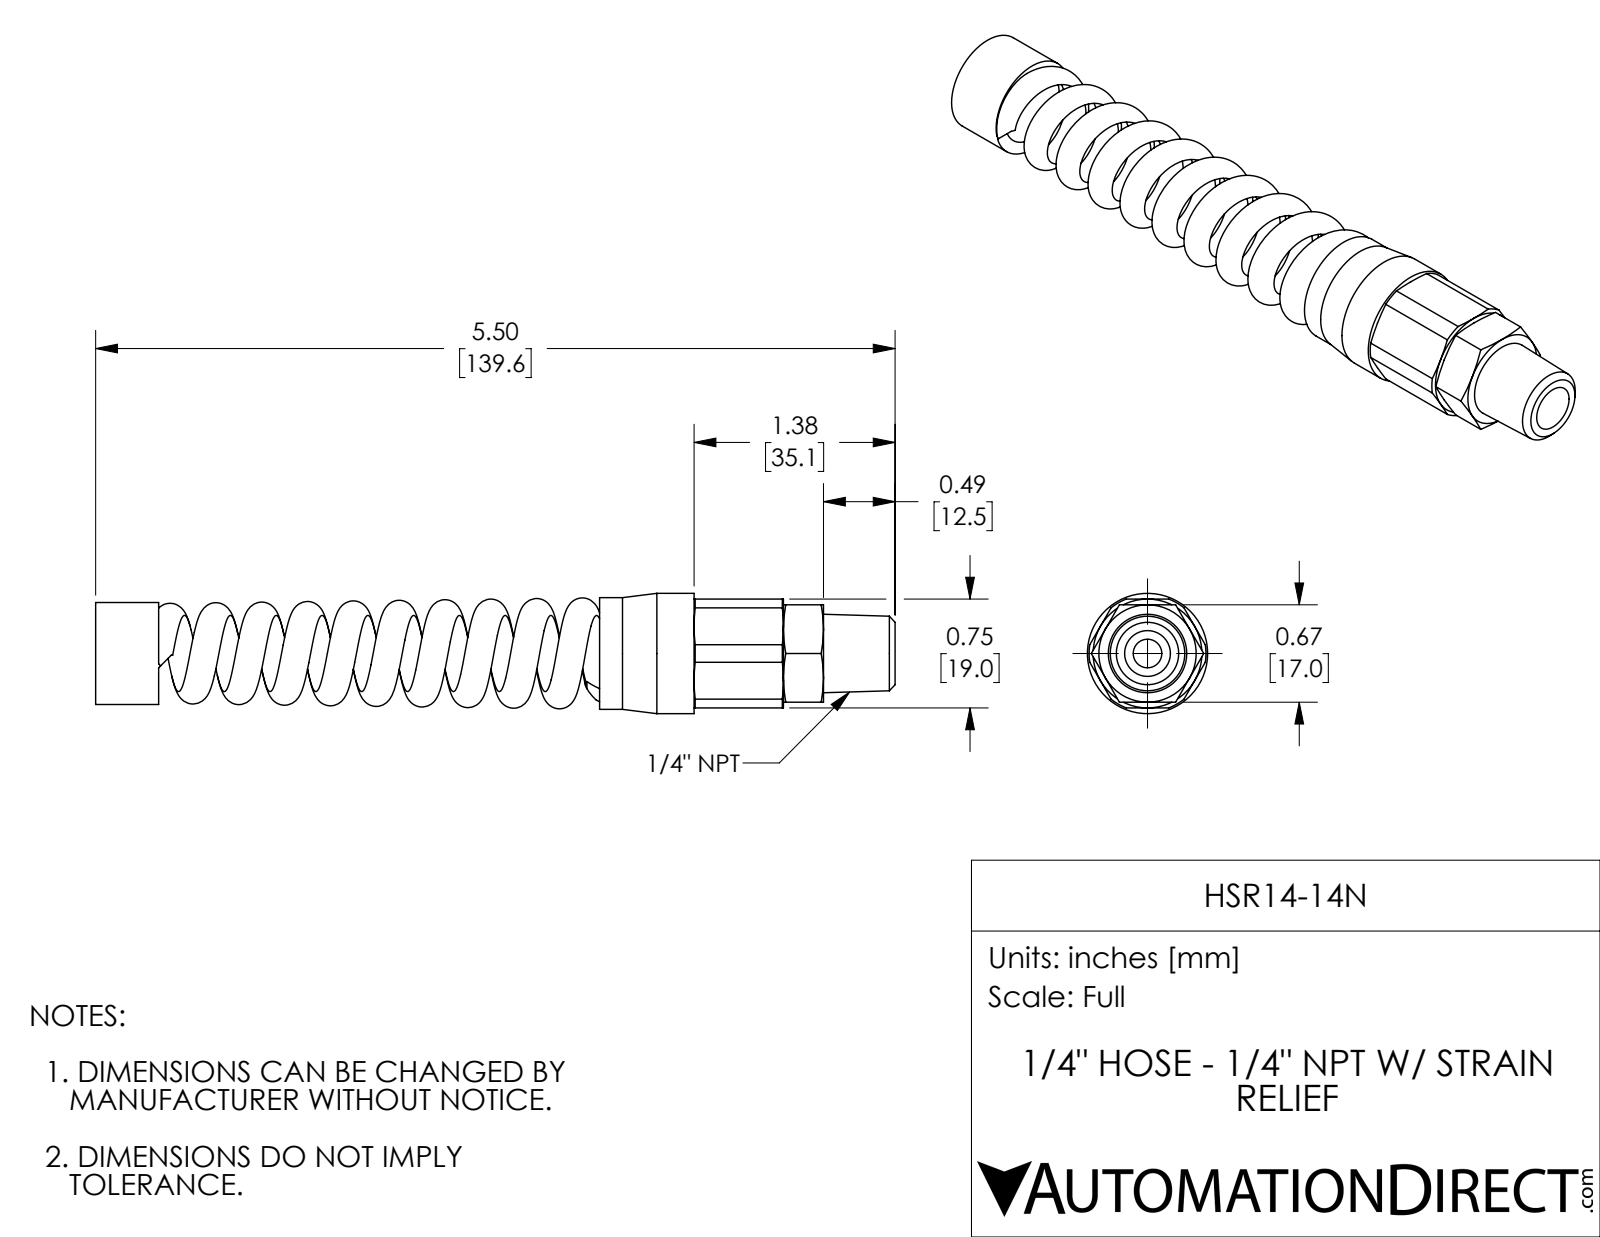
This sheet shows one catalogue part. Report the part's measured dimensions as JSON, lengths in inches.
{"part_name": "HSR14-14N", "step_written_by": "SolidWorks 2017 (AUTOMOTIVE_DESIGN)", "units": "inches", "bodies": {"solids": 3, "faces": 121, "planar": 33, "cylindrical": 49, "other": 39}, "overall_size": [5.496, 0.827, 0.827], "volume_in3": 0.906, "surface_area_in2": 24.97, "round_holes": [[0.197, 1], [0.315, 1], [0.524, 1], [0.591, 1], [0.63, 1], [0.709, 1]], "round_bosses_or_shafts": [[0.827, 1], [0.768, 1], [0.701, 1], [0.62, 1], [0.295, 1]], "partial_cylinders_radius": [[0.402, 1]], "face_to_face_distances": [0.039, 0.709, 0.748, 0.669, 0.65, 0.614, 0.354, 0.26, 0.472, 0.732]}
